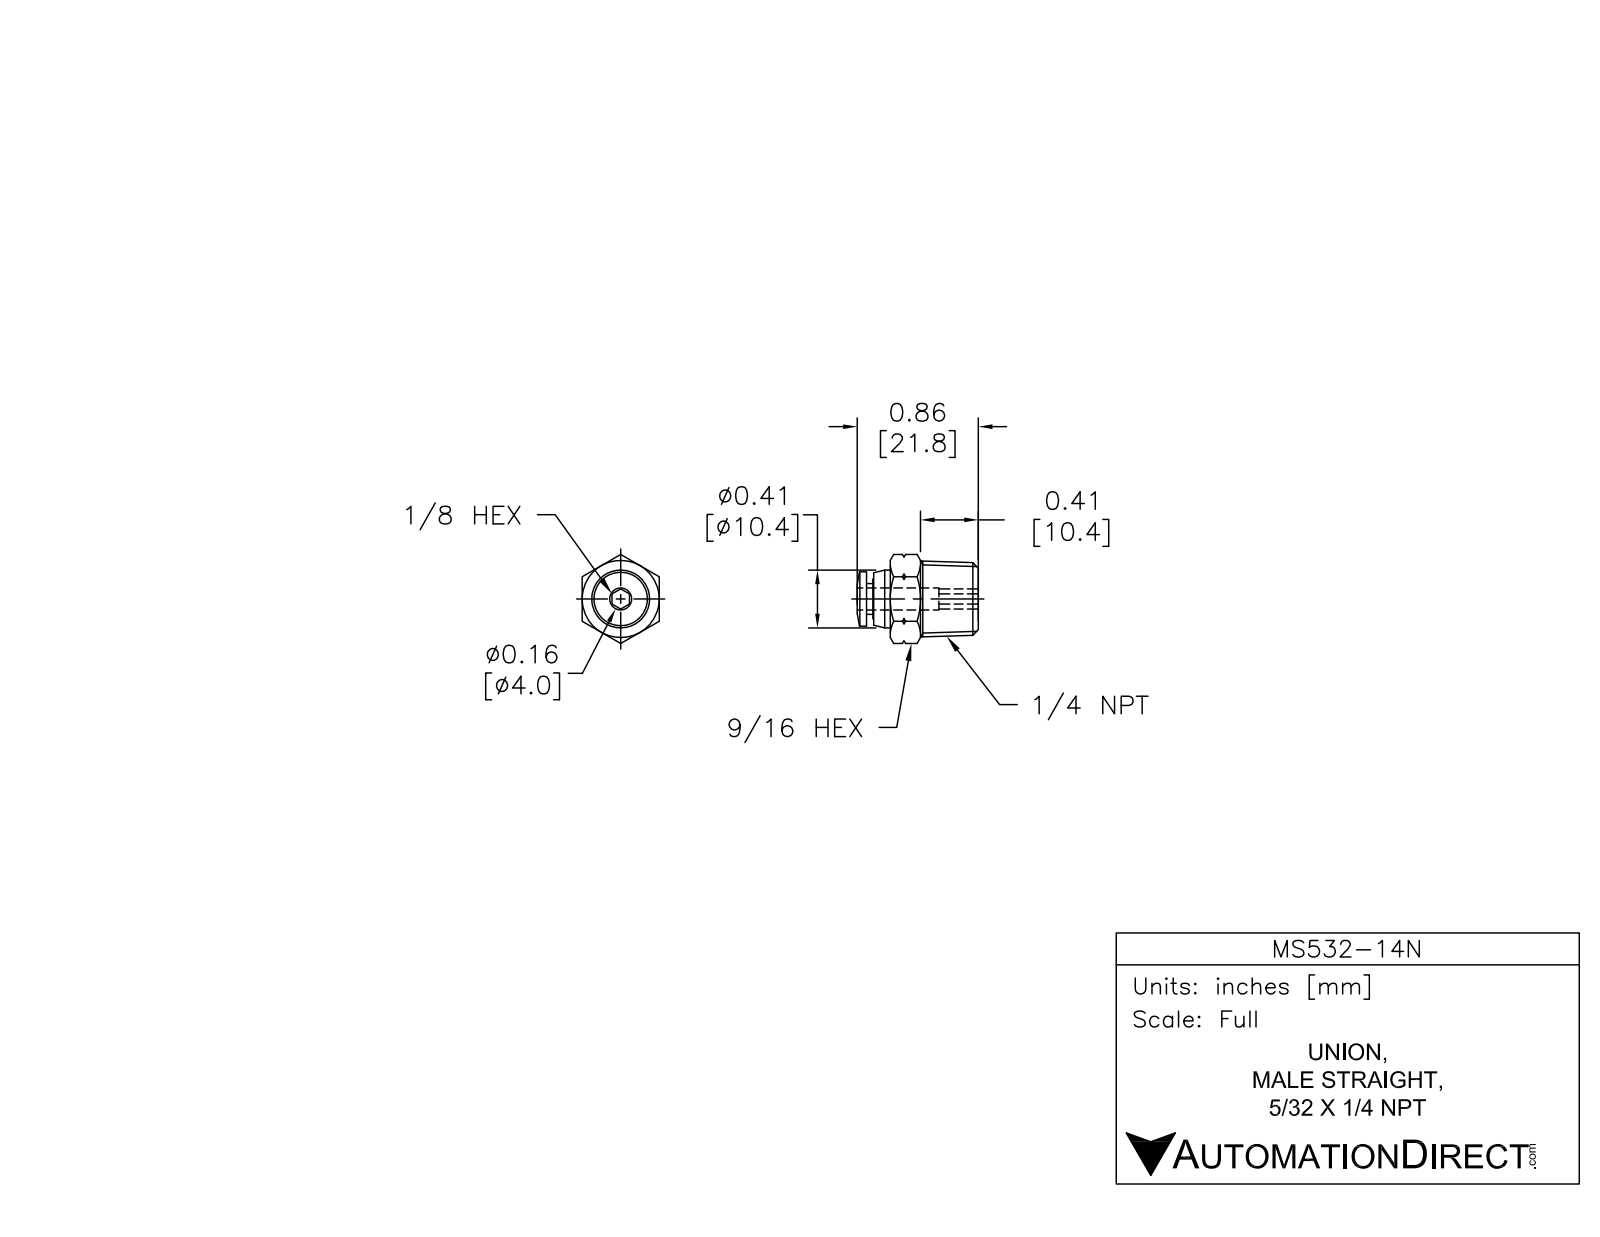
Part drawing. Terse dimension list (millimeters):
name: PC5-32--N02
written by: Autodesk Inventor 2008 (AUTOMOTIVE_DESIGN)
unit: mm
bodies: 1 solid, 50 faces (13 planar, 6 cylindrical, 31 other)
size: 22 × 16.17 × 14
volume: 2 526 mm³; area: 1 501 mm²
holes: 1× ⌀3.2, 1× ⌀4.3
bosses: 1× ⌀10.5, 1× ⌀9.85, 1× ⌀7.2, 1× ⌀5.6
face distances: 14, 16, 20.3, 4.3, 19, 3, 1.3, 19.15, 3.15, 1.15
